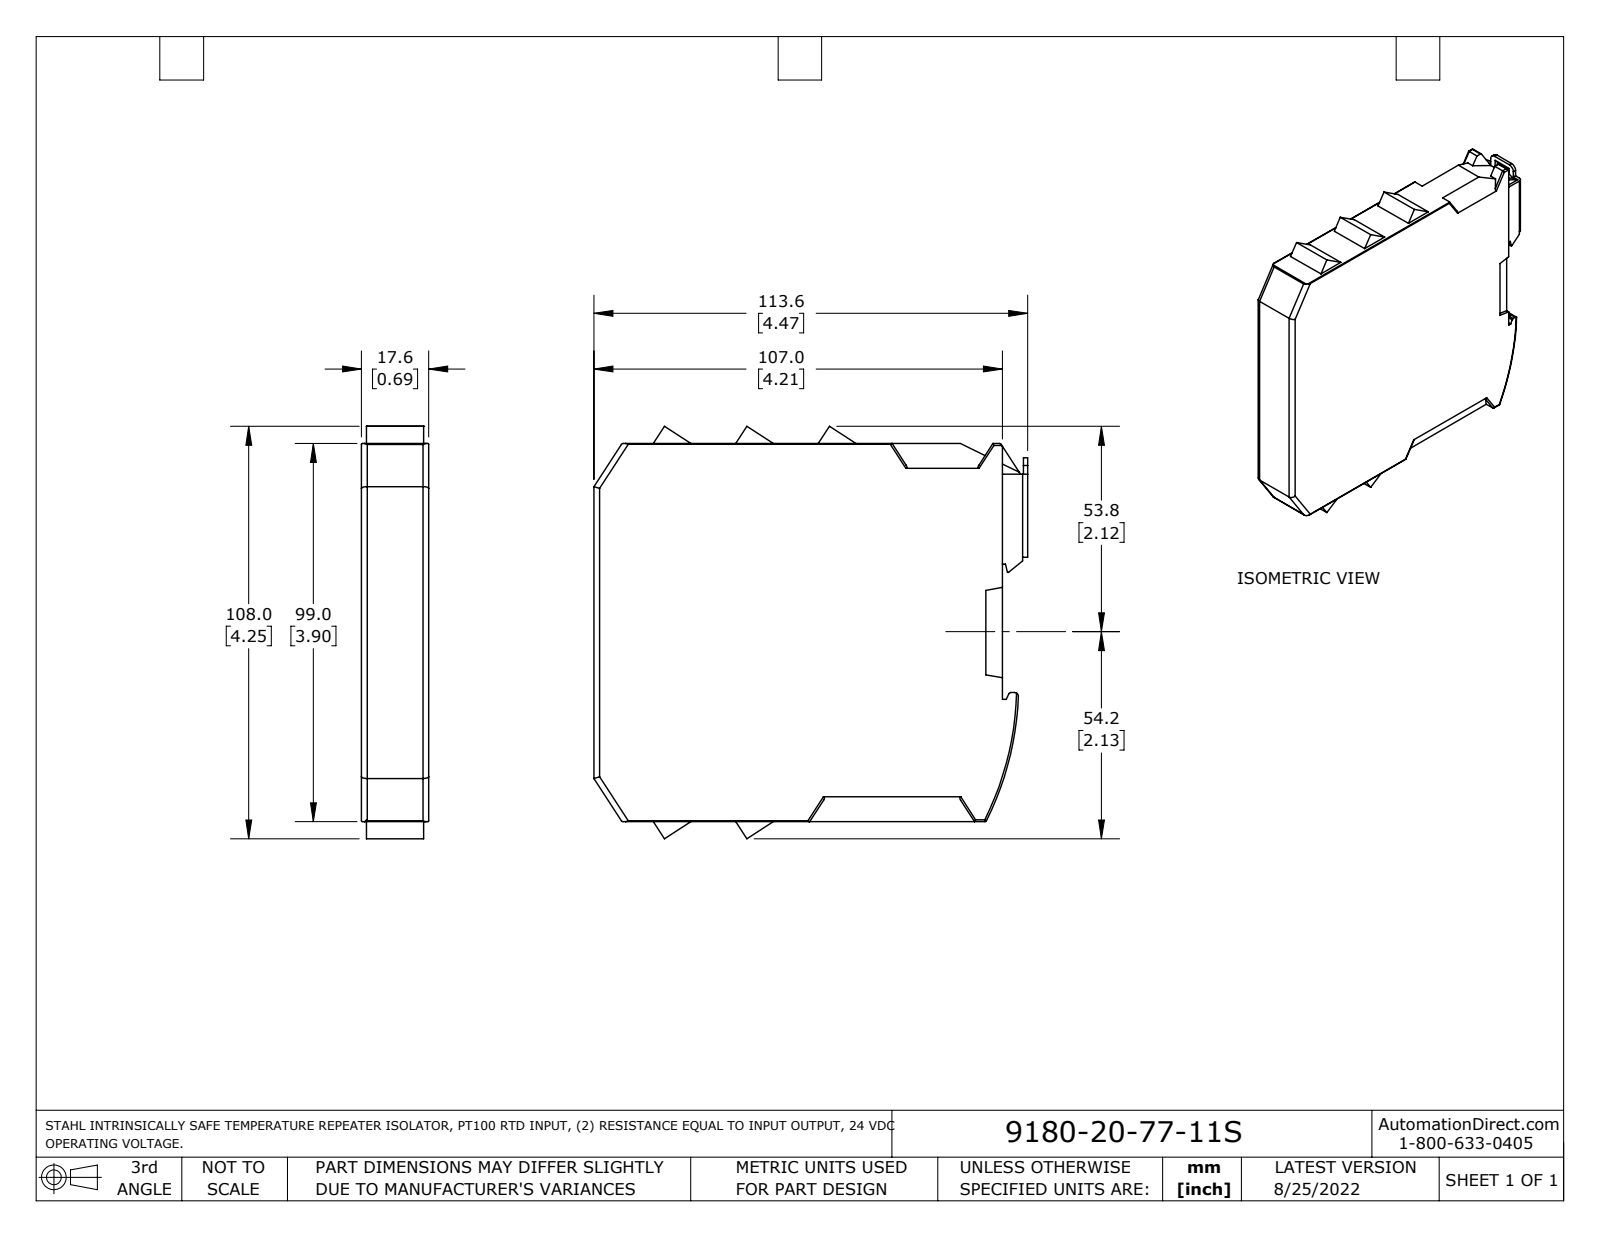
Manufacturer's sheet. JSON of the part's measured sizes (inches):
{"part_name": "9180-20-77-11S", "step_written_by": "SolidWorks 2021 (AUTOMOTIVE_DESIGN)", "units": "inches", "bodies": {"solids": 2, "faces": 181, "planar": 127, "cylindrical": 52, "other": 2}, "overall_size": [4.472, 4.252, 0.693], "volume_in3": 11.44, "surface_area_in2": 46.75, "partial_cylinders_radius": [[0.02, 17], [0.059, 6], [0.008, 4], [0.028, 4], [0.051, 2], [0.079, 2], [0.039, 1], [3.15, 1]], "face_to_face_distances": [0.693, 3.898, 4.213, 0.041, 0.652, 0.217, 4.429, 0.043, 0.26, 4.472]}
